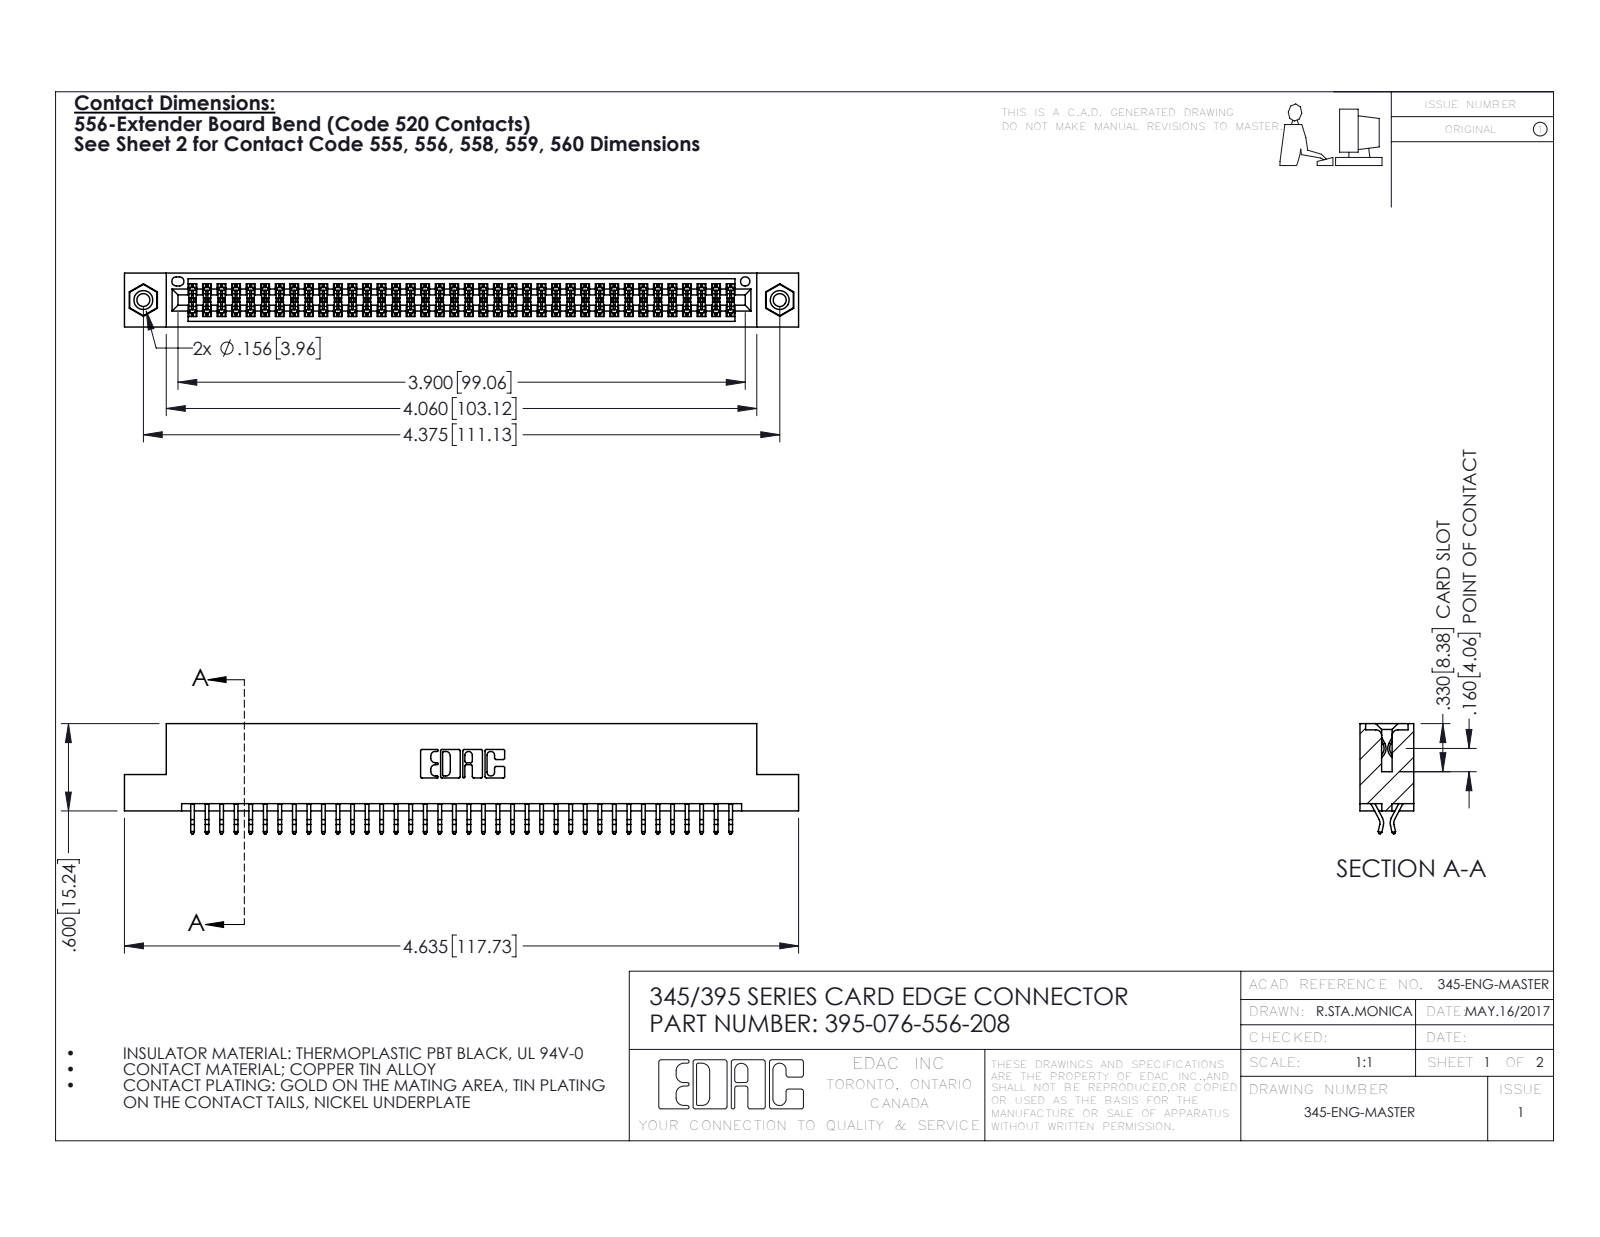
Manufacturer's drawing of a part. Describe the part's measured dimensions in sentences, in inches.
The part is named "395-076-556-208; 345-250-001_345-250-003-102; 345 Part_Flush Mounting Lugs - 0.156 Dia-TI; 345-292-001_556 Tail". Its 3-D file was written by "SolidWorks 2016 (CONFIG_CONTROL_DESIGN)". It is 79 solids with 4442 faces: 2924 planar, 1502 cylindrical and 16 other. Overall it measures 4.635 by 0.757 by 0.37 inches. Its volume is 0.695 cubic inches and its surface area 25.89 square inches. Round holes: 2 of diameter 0.089, 2 of diameter 0.125, 2 of diameter 0.156, 1 of diameter 0.064. Round bosses or shafts: 2 of diameter 0.155. Partial cylindrical surfaces (rounded edges, fillets, slot ends): 114 of radius 0.006, 22 of radius 0.01, 6 of radius 0.007, 6 of radius 0.031, 3 of radius 0.026, 2 of radius 0.01, 2 of radius 0.014, 2 of radius 0.019. The main face-to-face distances are 0.072, 0.298, 0.2, 0.37, 0.025, 0.098, 0.272, 0.225, 0.175, 0.149. The hole center spacings are 0.27, 4.139, 4.375.
